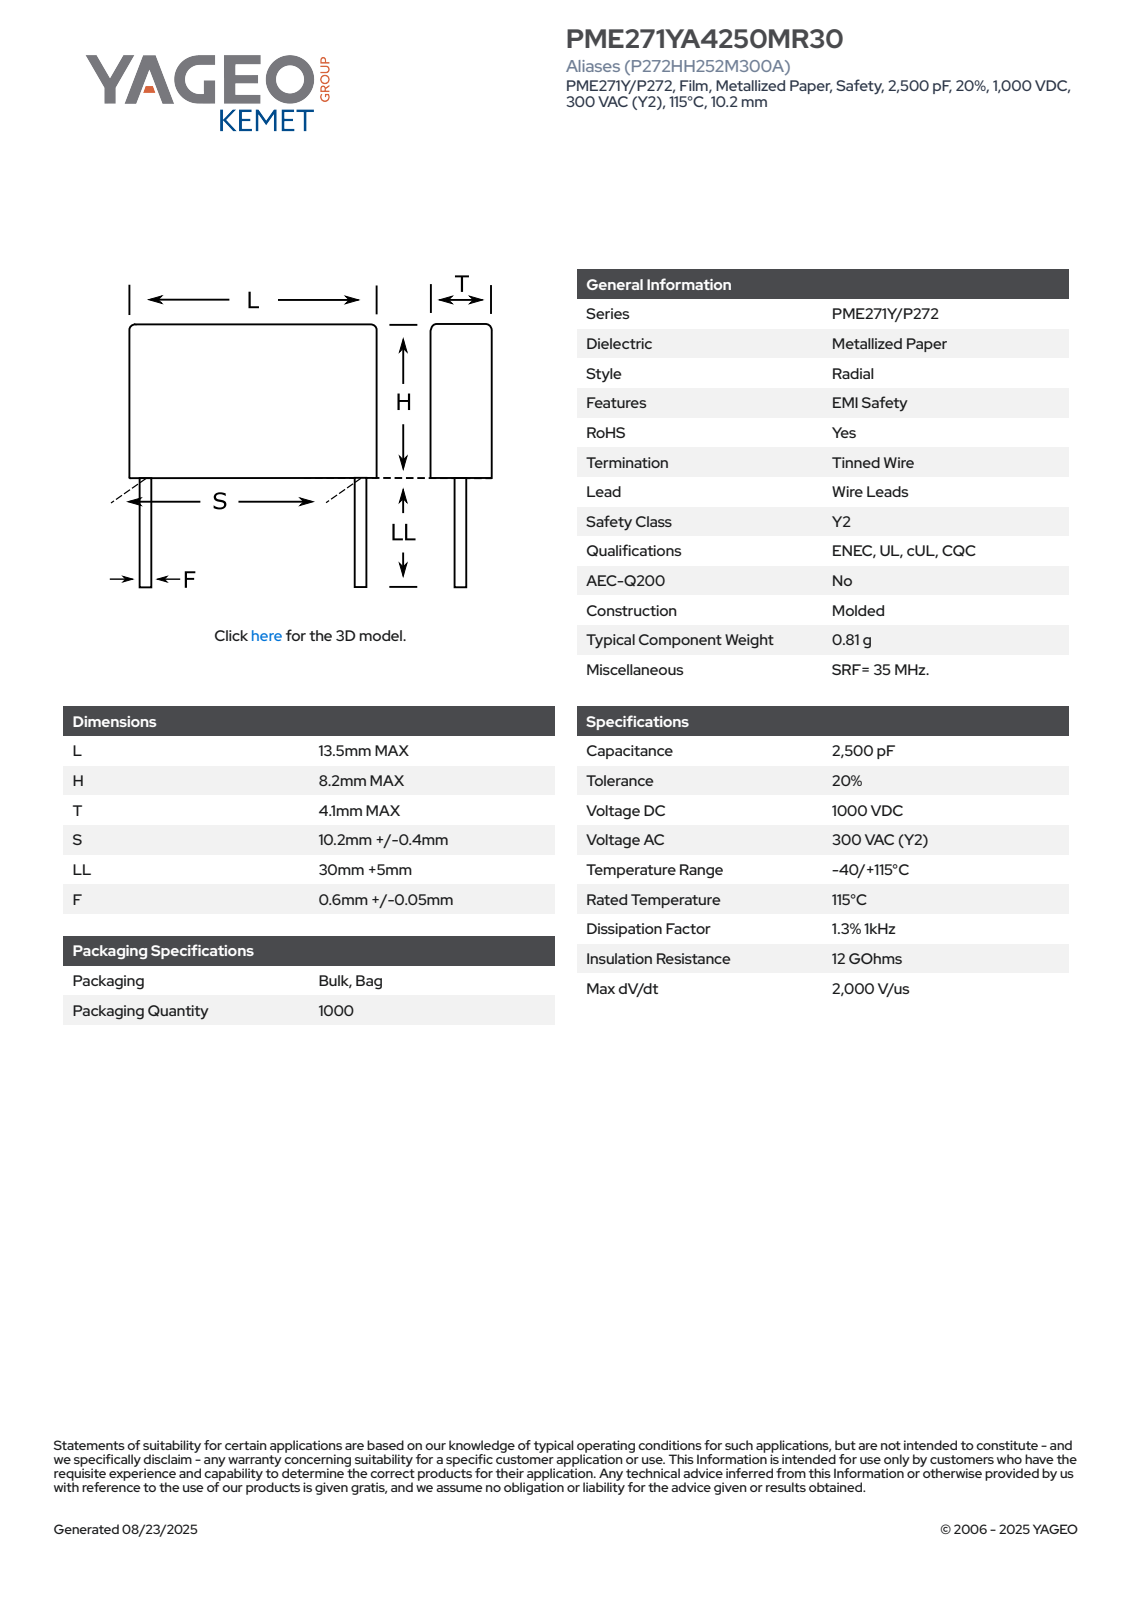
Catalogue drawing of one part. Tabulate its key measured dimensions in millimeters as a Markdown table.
| quantity | value |
| --- | --- |
| part name | CFR_MOLDED_13.5X8.2X4.1_L13.5H8.2T4.1S10.2LL35F0.65 |
| STEP written by | SolidWorks 2014 (AUTOMOTIVE_DESIGN) |
| units | millimeters |
| bodies | 4 solids, 73 faces (65 planar, 8 cylindrical, 0 other) |
| overall size | 43.2 × 13.5 × 4.11 |
| volume | 475 mm³ |
| surface area | 543 mm² |
| round bosses / shafts (diameter × count) | 0.65 × 2 |
| partial cylindrical surfaces (radius × count) | 0.5 × 4 |
| main face-to-face distances | 4.1, 8.2, 13.5, 35, 43.2, 39.65, 4.65, 3.55, 38.44, 3.44 |
